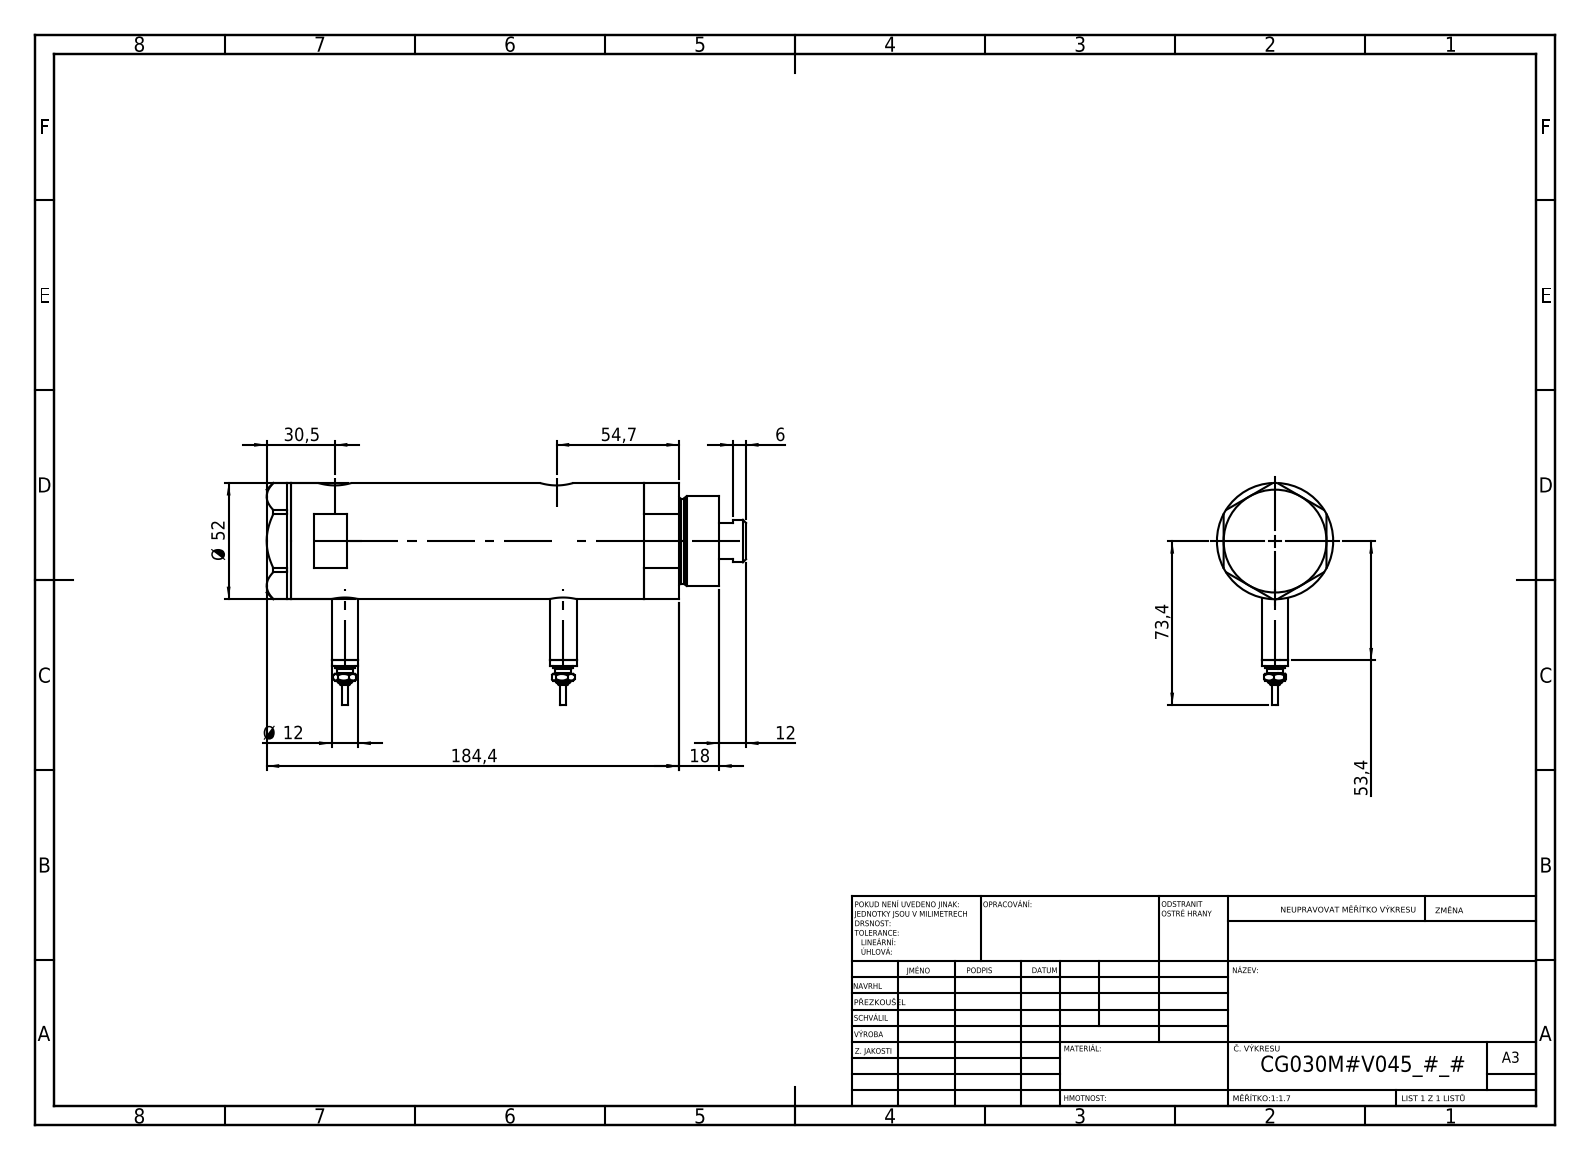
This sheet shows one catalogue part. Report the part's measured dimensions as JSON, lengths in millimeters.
{"part_name": "V270CG_BACK; V270CG_FRONT; Switch; V270CG_MIDDLE (+1 more)", "step_written_by": "SolidWorks 2019 (CONFIG_CONTROL_DESIGN)", "units": "millimeters", "bodies": {"solids": 6, "faces": 226, "planar": 93, "cylindrical": 69, "other": 64}, "overall_size": [214.4, 99.4, 52], "volume_mm3": 398755, "surface_area_mm2": 89998, "round_holes": [[9.73, 2], [12.5, 2], [15, 2], [6.5, 1], [20, 1], [21.5, 1], [30, 1], [33, 1], [44, 1]], "round_bosses_or_shafts": [[12, 2], [9, 2], [7, 2], [4.5, 2], [2.5, 2], [52, 1], [40, 1], [38, 1]], "face_to_face_distances": [121.5, 23.8, 97.7, 11, 34.8, 132.5, 46, 36.4, 168.9, 157.9], "hole_center_spacings": [2.9, 4.5, 94.7, 97.6, 99.2, 102.1]}
